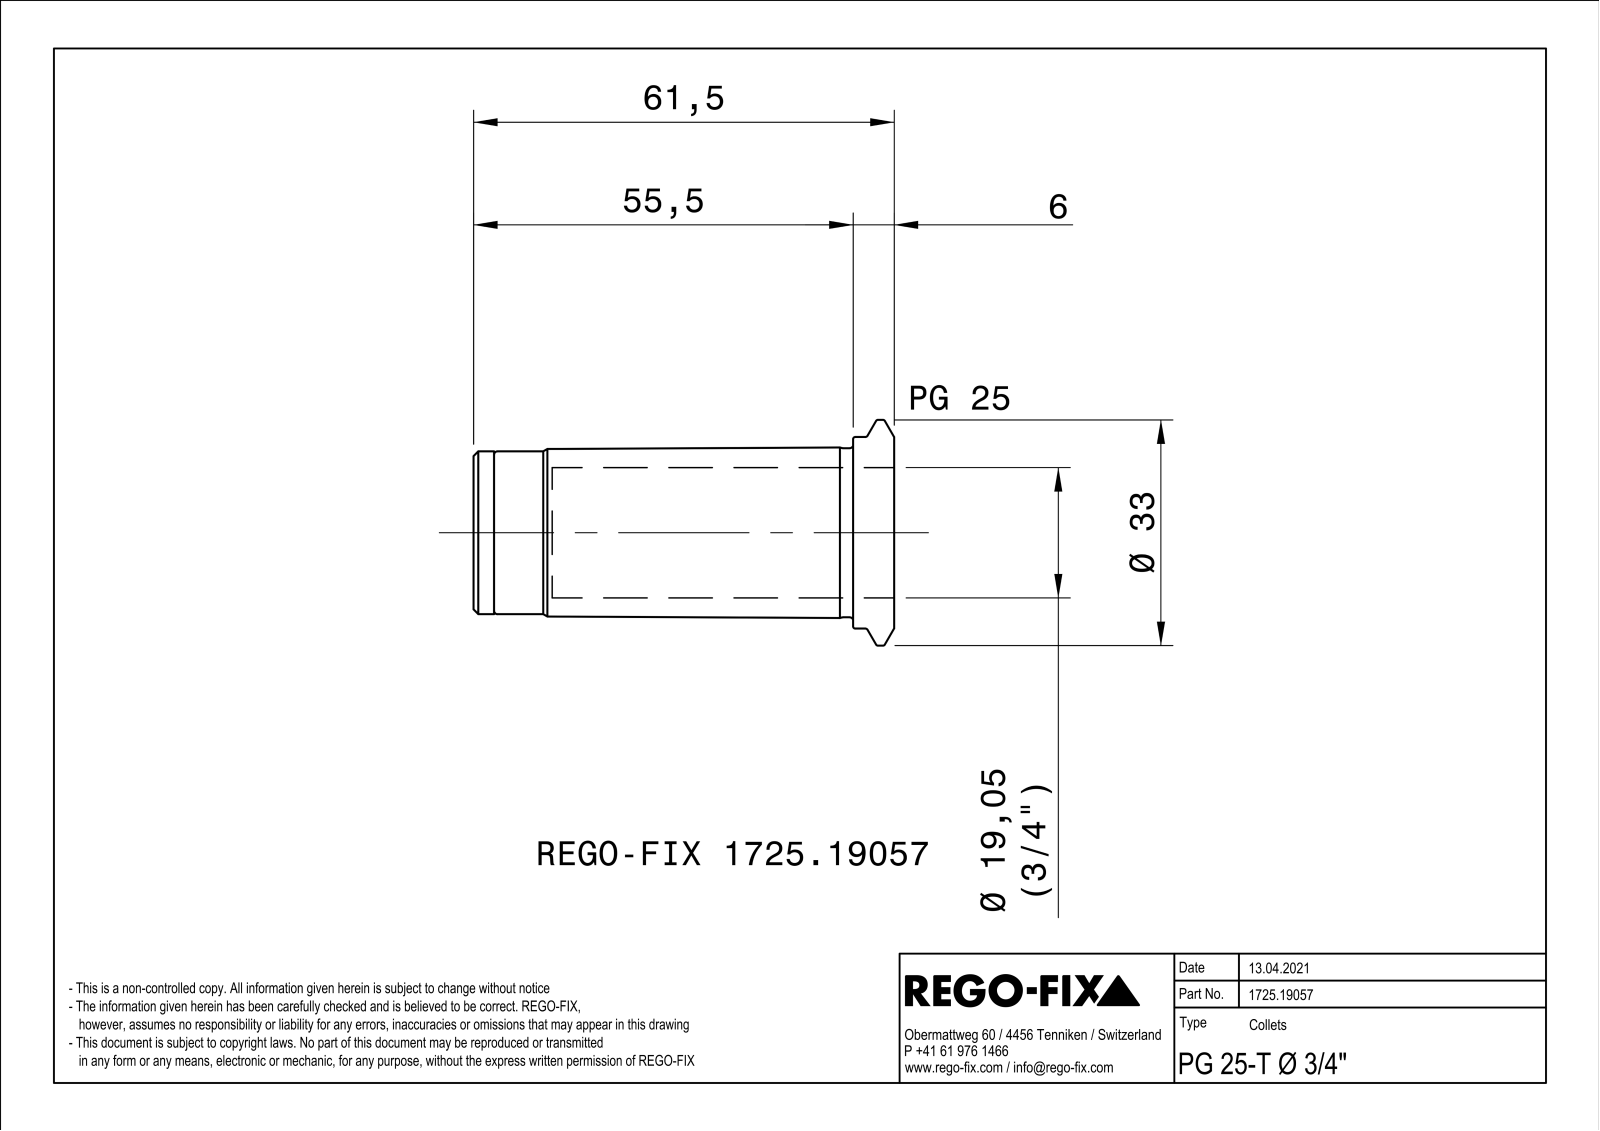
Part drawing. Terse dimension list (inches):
name: NOCUT
written by: SIEMENS PLM Software Solid Edge ST10 (AUTOMOTIVE_DESIGN)
unit: in
bodies: 0 solids, 82 faces (24 planar, 20 cylindrical, 38 other)
size: 2.303 × 1.299 × 1.297
holes: 1× ⌀0.128, 1× ⌀0.75, 1× ⌀0.827, 1× ⌀0.866
bosses: 1× ⌀1.299, 1× ⌀1.102, 1× ⌀0.972, 1× ⌀0.937
rounds: 1× R0.085, 1× R0.16, 1× R0.164
face distances: 0.039, 0.236, 2.201, 2.244, 1.965, 2.008, 0.043, 2.303, 2.067, 0.102
